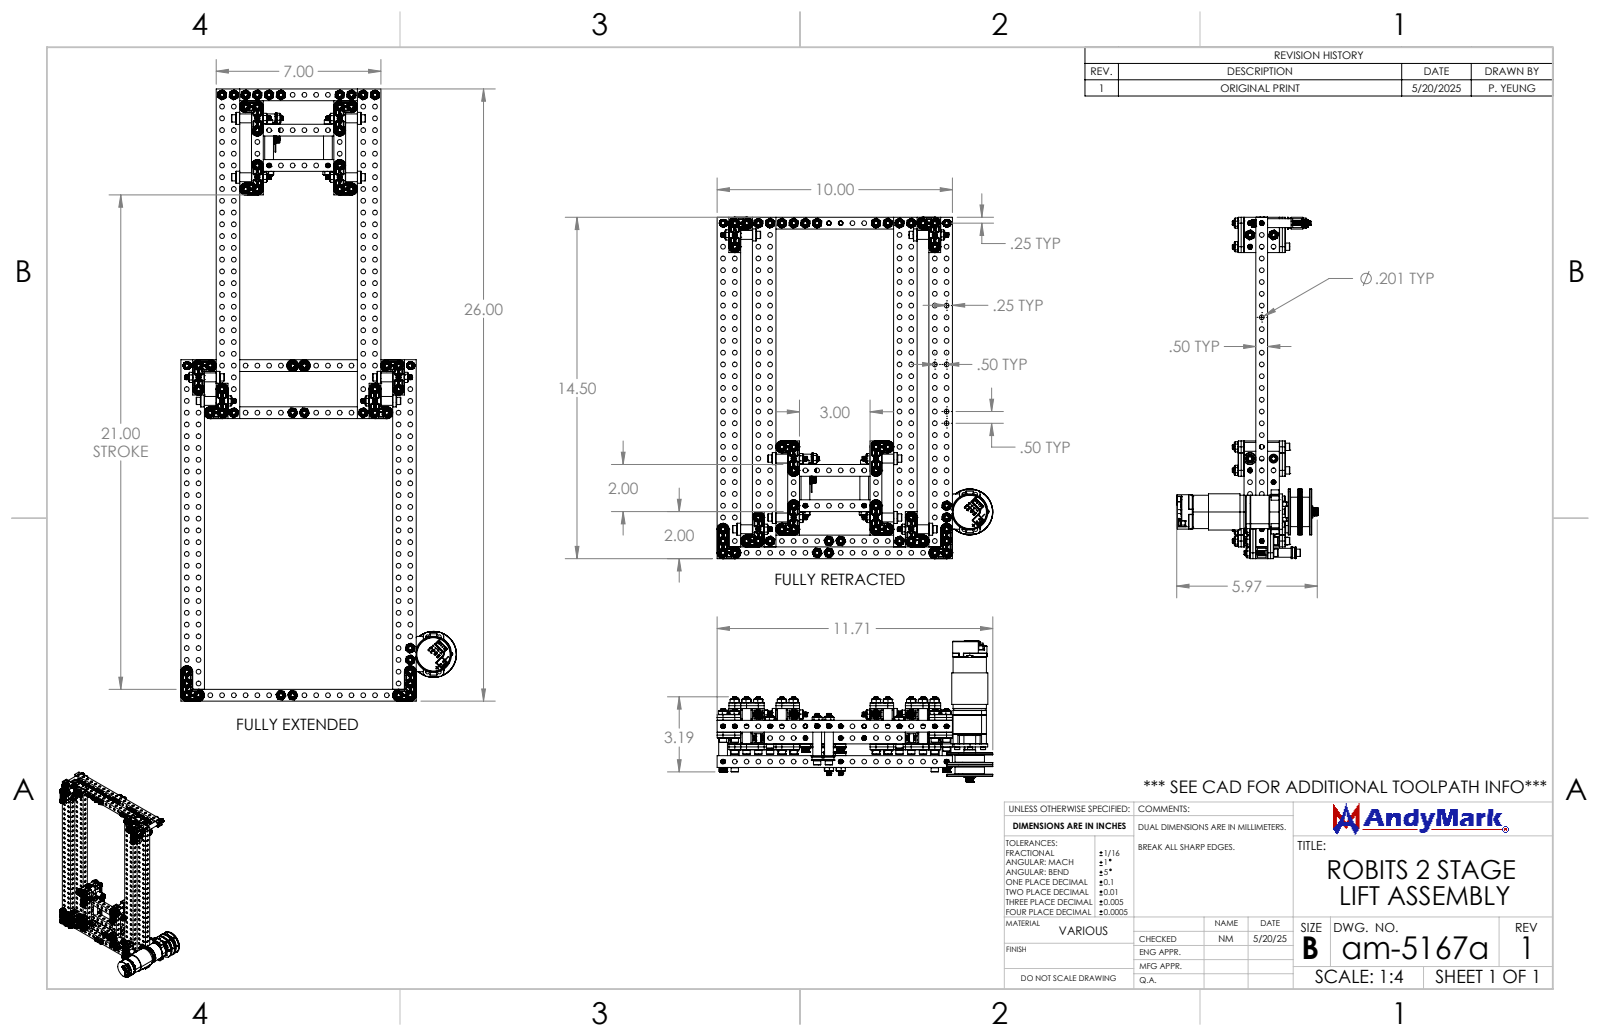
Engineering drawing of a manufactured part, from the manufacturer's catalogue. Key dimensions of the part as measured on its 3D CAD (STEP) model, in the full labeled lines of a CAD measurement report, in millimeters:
Part name (STEP PRODUCT): am-1041 10-32 x 1250 SHCS_am-1041 10-32 x 1250 SHCS; am-1002 10-32 x 0500 SHCS_am-1002 10-32 x 0500 SHCS; am-1742 0.430 ID 0.500 OD 0.125 Long Aluminum Spacer; NeveRest Hex Output Block (+8 more)
STEP written by: SolidWorks 2024 (AUTOMOTIVE_DESIGN)
Units: millimetres
Bodies: 1102 solids, 45150 faces (7456 planar, 16047 cylindrical, 21647 other)
Overall size (bounding box): 368.5 × 297.5 × 152
Volume: 568 300 mm³ · Surface area: 671 600 mm²
Round holes (diameter × count): ⌀5.1 ×408, ⌀4.2 ×280, ⌀4.1 ×62, ⌀6.1 ×62, ⌀4.9 ×30, ⌀5 ×24, ⌀8.2 ×16, ⌀9.8 ×16, ⌀2.5 ×10, ⌀0.6 ×9, ⌀3.2 ×8, ⌀6.5 ×8
Round bosses / shafts (diameter × count): ⌀4.8 ×65, ⌀7.9 ×52, ⌀9.5 ×31, ⌀13 ×16, ⌀8 ×13, ⌀12.6 ×8, ⌀11 ×8, ⌀10.7 ×8
Partial cylindrical surfaces — rounded edges, fillets, slot ends (radius × count): R0.3 ×804, R0.1 ×92, R0.1 ×74, R0.3 ×74, R2.1 ×70, R0.5 ×59, R0.2 ×57, R0.8 ×32
Main face-to-face distances: 12.7, 1.6, 25.4, 38.1, 11.1, 23.8, 14.3, 9.5, 11.1, 1.6
Hole centre spacings: 25.4, 12.7, 38.1, 63.5, 50.8, 76.2, 88.9, 101.6
